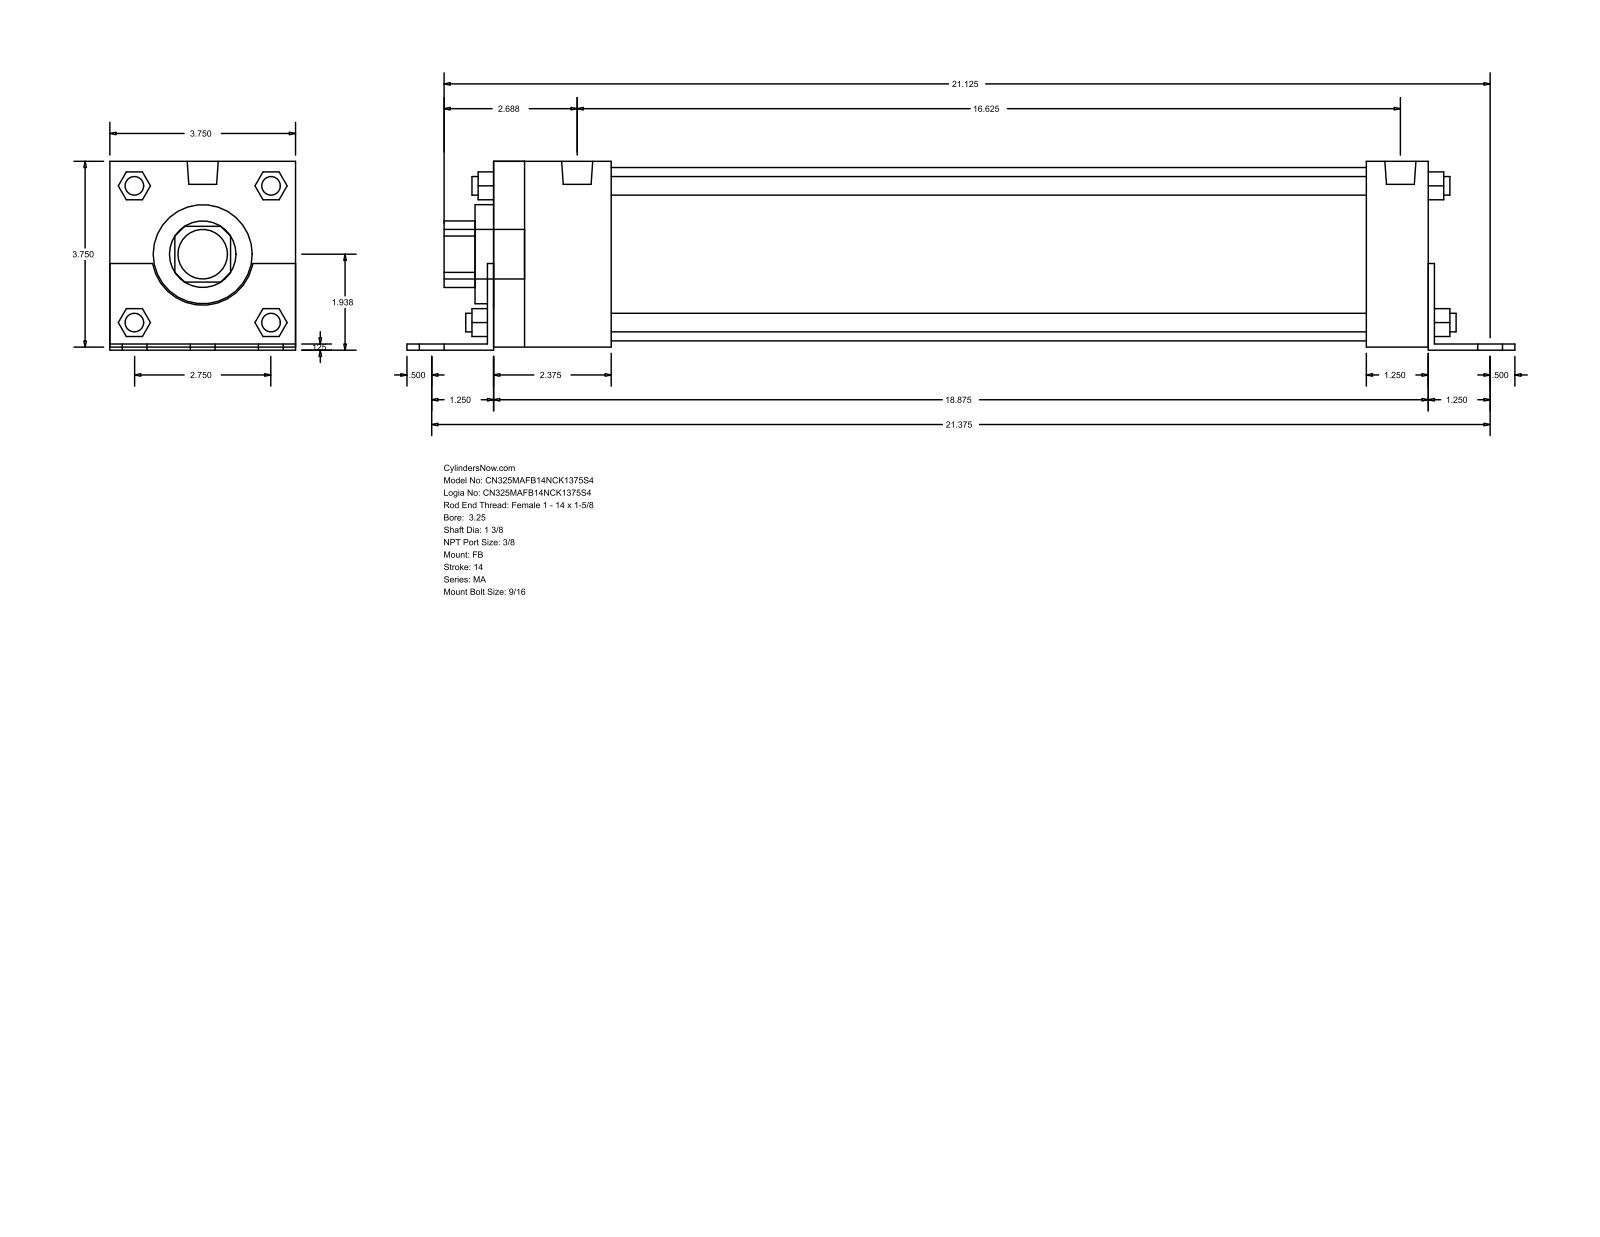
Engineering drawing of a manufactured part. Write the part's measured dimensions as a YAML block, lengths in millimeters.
part_name: "MA_FB__0325_1.375"
step_written_by: "GSSL Pune (CONFIG_CONTROL_DESIGN)"
units: millimeters
bodies: {solids: 0, faces: 140, planar: 105, cylindrical: 35, other: 0}
overall_size: [568.33, 96.84, 95.25]
round_holes:
  - {diameter: 34.92, count: 1}
  - {diameter: 50.8, count: 1}
  - {diameter: 88.9, count: 1}
round_bosses_or_shafts:
  - {diameter: 14.29, count: 6}
  - {diameter: 11.11, count: 4}
  - {diameter: 9.53, count: 4}
  - {diameter: 15.93, count: 2}
  - {diameter: 25.4, count: 1}
partial_cylinders:
  - {radius: 17.06, count: 1}
  - {radius: 26.16, count: 1}
face_to_face_distances: [95.24, 3.17, 1.59, 96.83, 1.58, 93.66, 3.18, 479.42, 482.6, 31.75]
